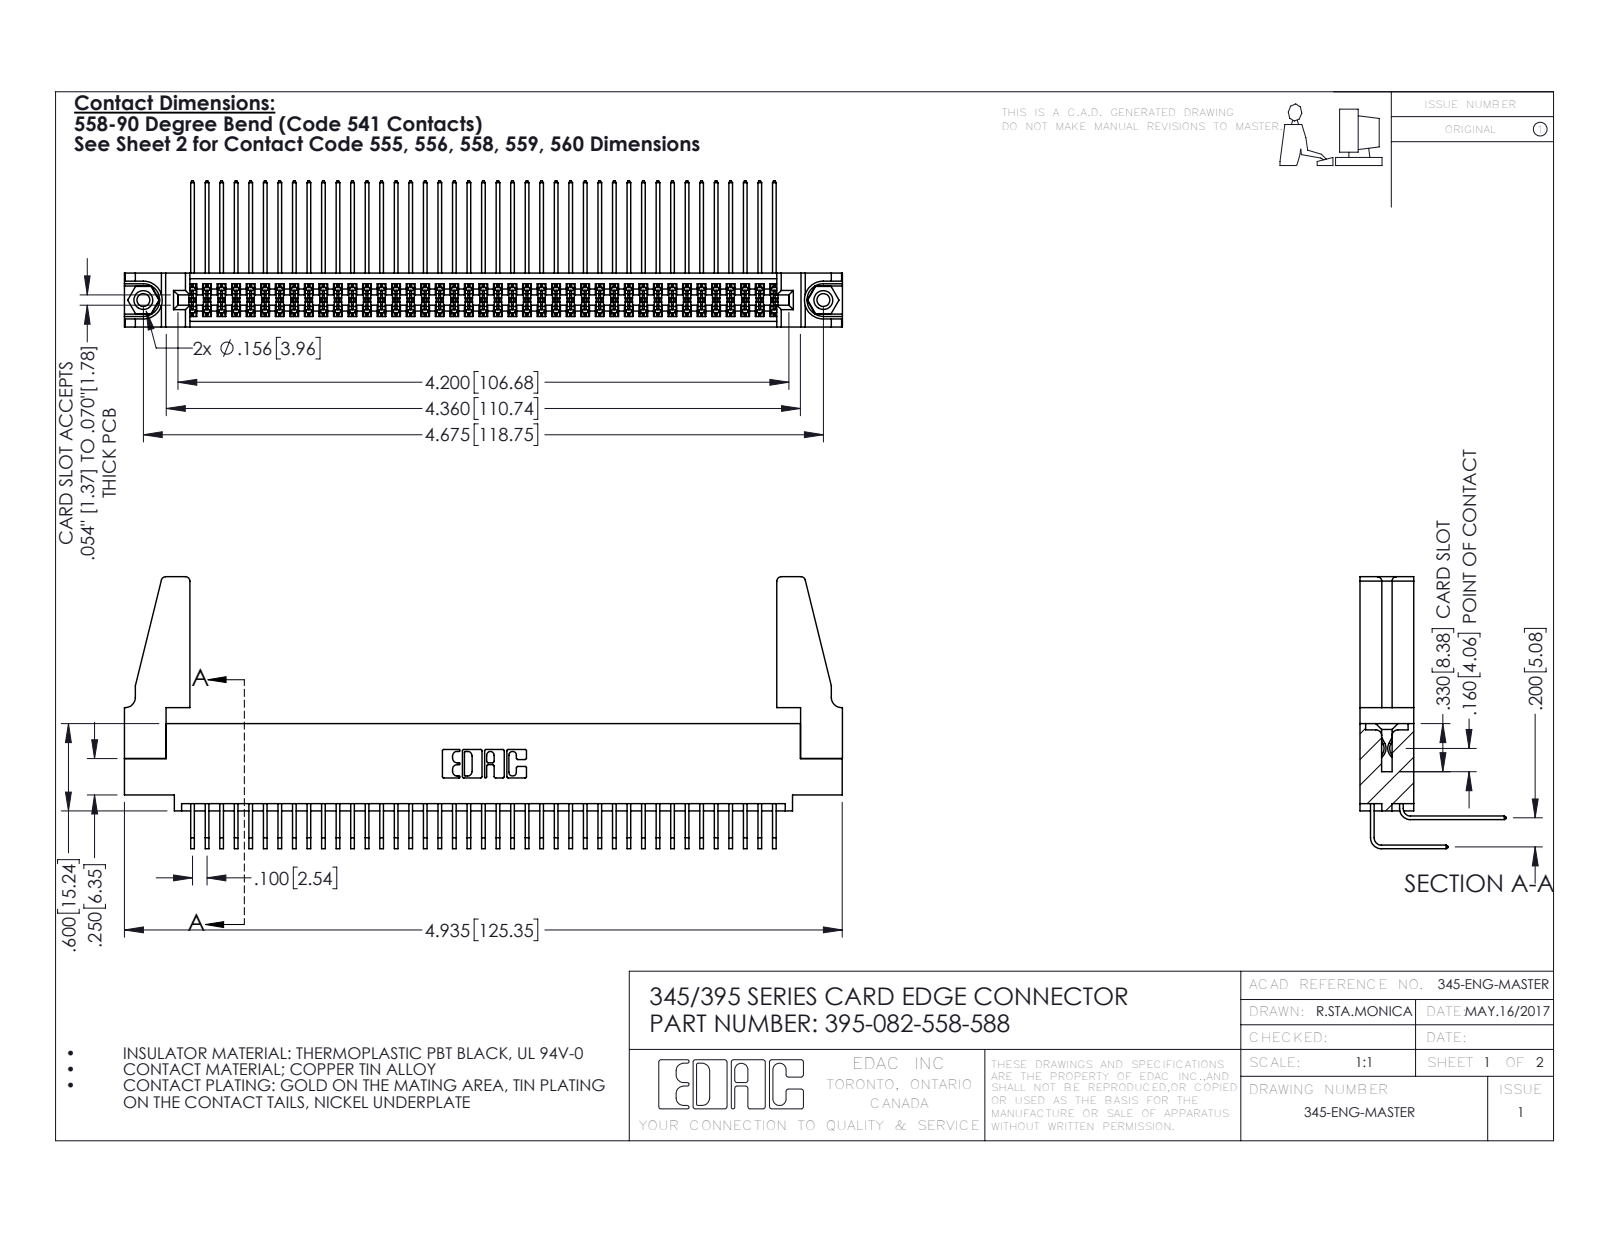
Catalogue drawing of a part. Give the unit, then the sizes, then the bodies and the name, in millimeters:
Units: millimetres
Overall size (bounding box): 125.4 × 47.5 × 25.5
Round holes (diameter × count): ⌀2.3 ×2, ⌀3.2 ×2, ⌀4 ×2, ⌀1.6 ×1
Round bosses / shafts (diameter × count): ⌀3.9 ×2
Partial cylindrical surfaces — rounded edges, fillets, slot ends (radius × count): R0.2 ×124, R0.3 ×22, R0.8 ×8, R0.2 ×6, R0.8 ×6, R0.7 ×3, R0.4 ×2, R0.5 ×2
Main face-to-face distances: 1.8, 7.6, 5.1, 9.4, 2.5, 6.9, 0.6, 5.7, 0.6, 4.4
Hole centre spacings: 6.9, 112.8, 118.7
Volume: 15 800 mm³ · Surface area: 24 000 mm²
Bodies: 87 solids, 4518 faces (3026 planar, 1476 cylindrical, 16 other)
Part name (STEP PRODUCT): 395-082-558-588; 345-292-001_558 Tail - 2; 345-250-001_345-250-001-102; 345-220-078_345-220-088 (+2 more)
STEP written by: SolidWorks 2016 (CONFIG_CONTROL_DESIGN)
